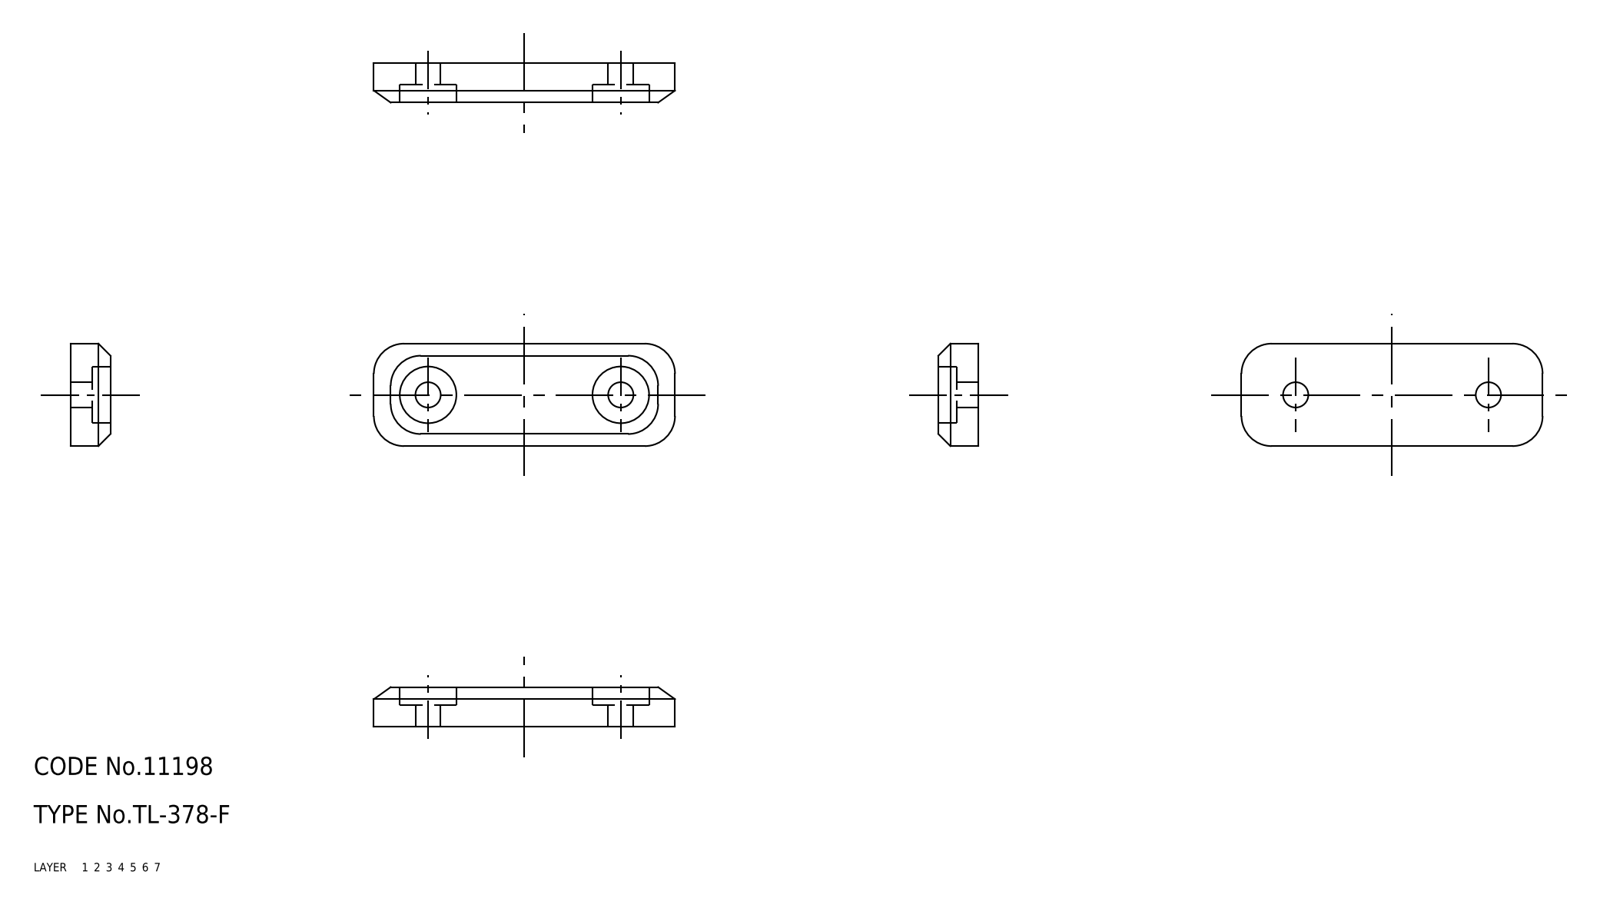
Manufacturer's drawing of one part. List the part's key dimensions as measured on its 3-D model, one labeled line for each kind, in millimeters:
Part name (STEP PRODUCT): TL_378_F; magnet
STEP written by: SolidWorks 2015 (AUTOMOTIVE_DESIGN)
Units: millimetres
Bodies: 1 solid, 28 faces (12 planar, 16 cylindrical, 0 other)
Overall size (bounding box): 50 × 17 × 6.6
Volume: 4 696 mm³ · Surface area: 2 547 mm²
Round holes (diameter × count): ⌀4.2 ×2, ⌀9.4 ×2
Partial cylindrical surfaces — rounded edges, fillets, slot ends (radius × count): R5 ×8
Main face-to-face distances: 6.6, 17, 3, 3.6, 50
Hole centre spacings: 32
